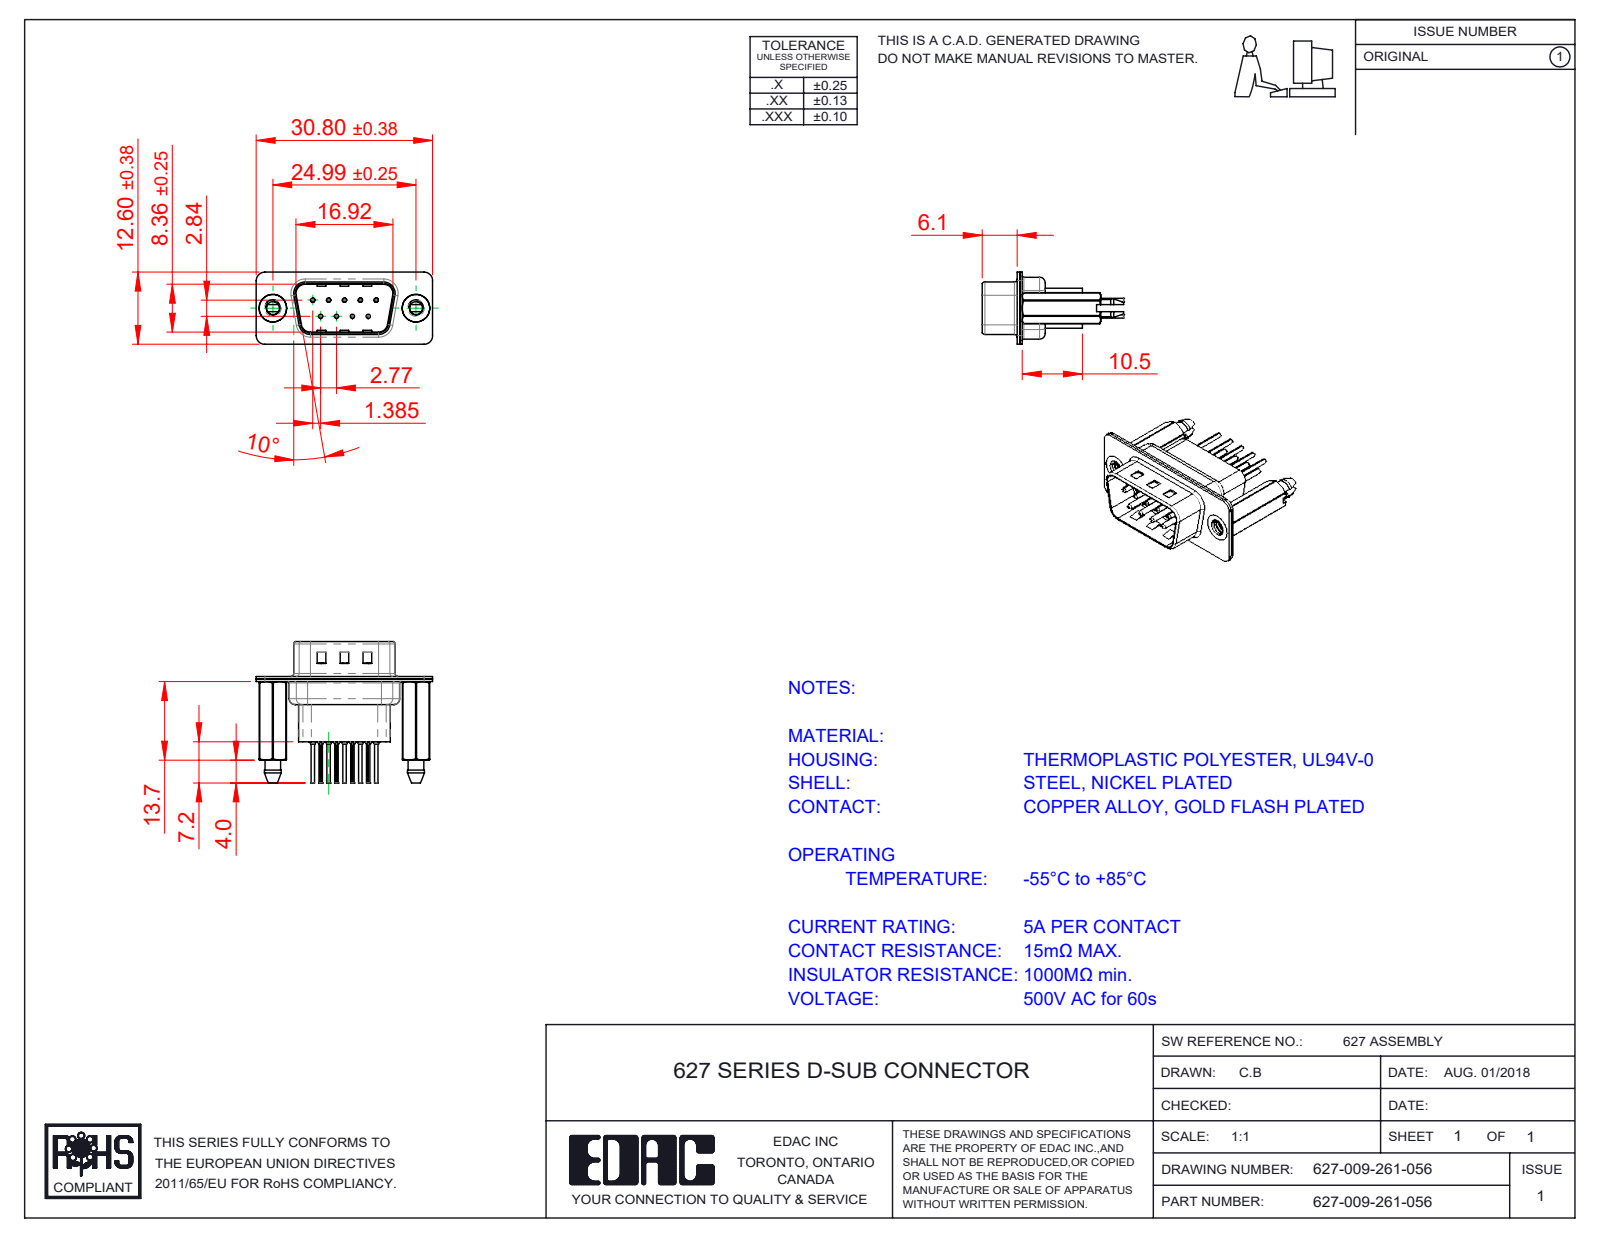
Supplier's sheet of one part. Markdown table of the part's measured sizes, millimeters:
| quantity | value |
| --- | --- |
| part name | 627 Housing_09 HP; 627 Contact Row 2_61; 627-009-261-056; 627 Contact Row 1_61 (+3 more) |
| STEP written by | SolidWorks 2020 (CONFIG_CONTROL_DESIGN) |
| units | millimeters |
| bodies | 14 solids, 1294 faces (355 planar, 528 cylindrical, 411 other) |
| overall size | 30.8 × 24.6 × 12.6 |
| volume | 2 123 mm³ |
| surface area | 5 516 mm² |
| round holes (diameter × count) | 0.2 × 9, 0.35 × 9, 1.1 × 9, 1.6 × 9, 2.26 × 2, 4 × 2, 4.8 × 2 |
| round bosses / shafts (diameter × count) | 2 × 9, 1.5 × 9, 0.75 × 9, 0.6 × 9, 4.9 × 2 |
| partial cylindrical surfaces (radius × count) | 1.5 × 20, 0.1 × 18, 2 × 12, 1.6 × 10, 0.5 × 8, 0.25 × 4, 0.6 × 4, 0.65 × 4 |
| main face-to-face distances | 0.45, 0.4, 0.9, 0.82, 9.58, 1.4, 4.76, 1.5, 0.68, 7.68 |
| hole center spacings | 3.16, 2.77, 5.54, 5.03, 5.04, 8.31, 7.48, 7.49 |
